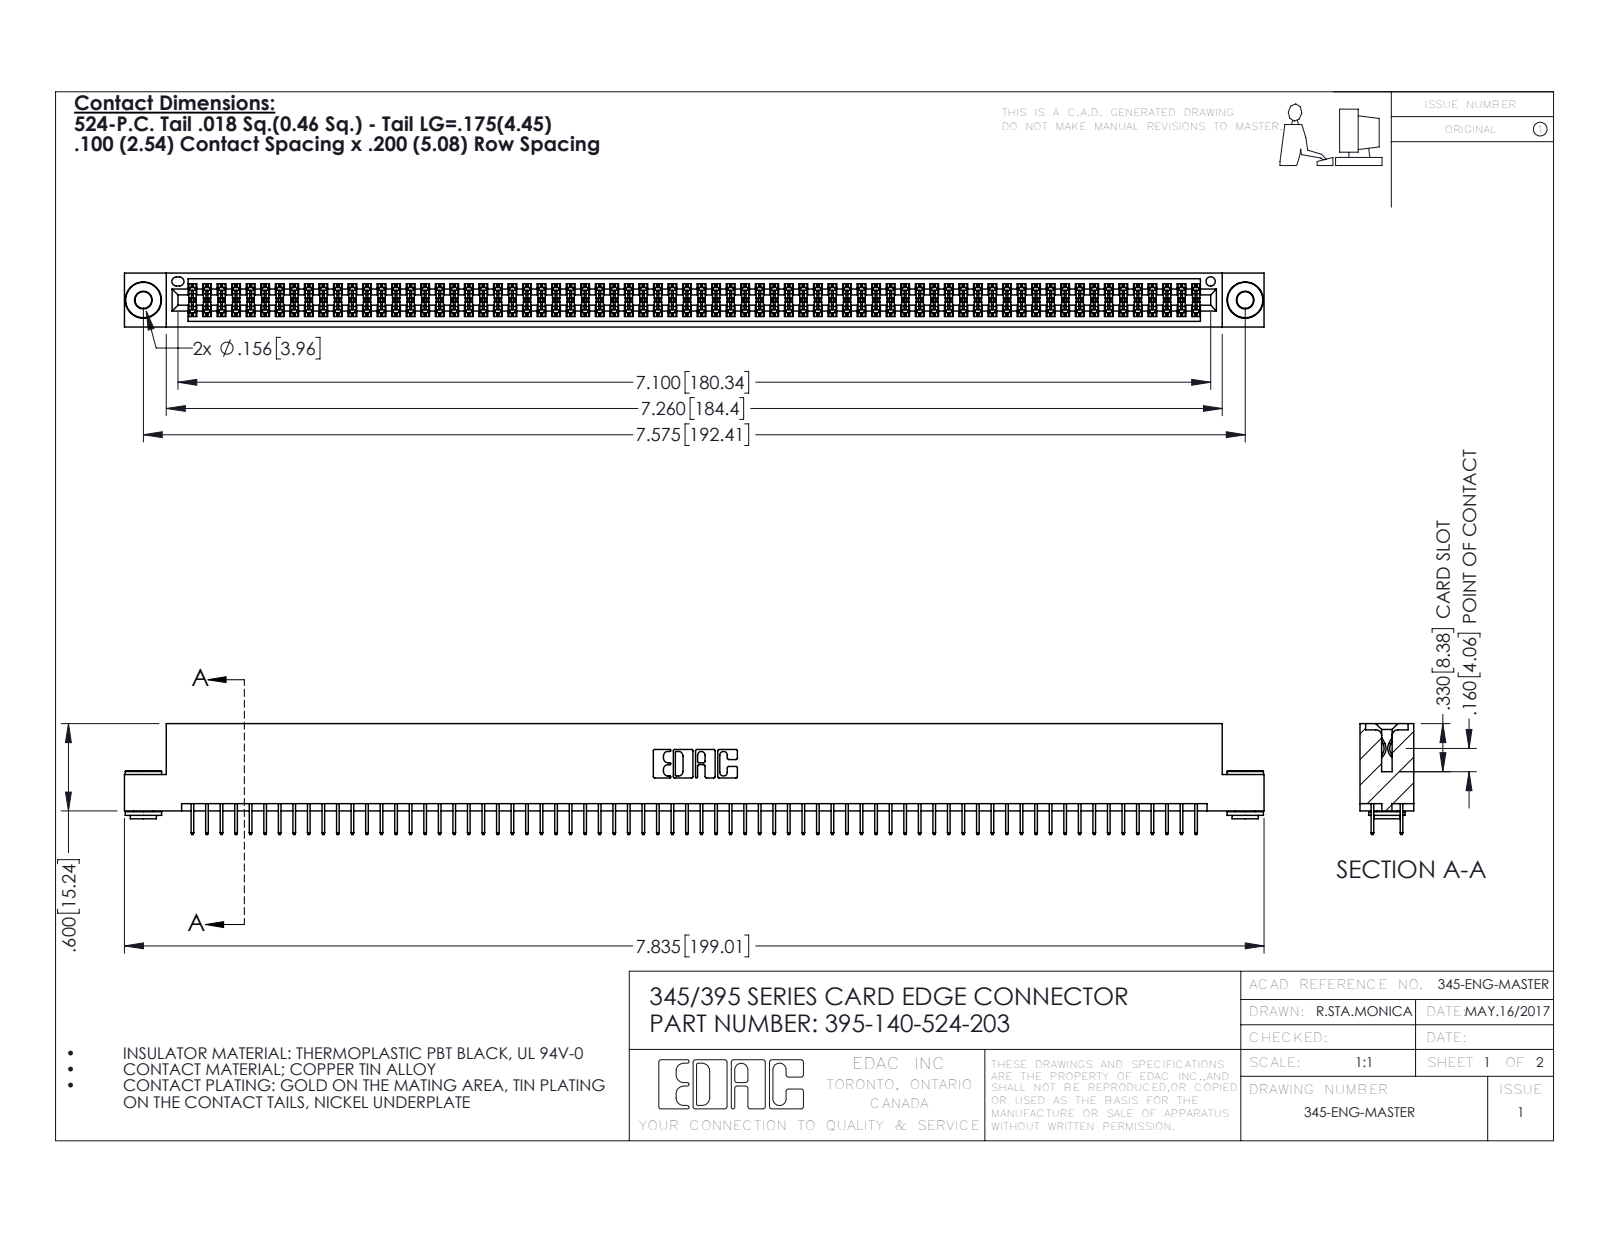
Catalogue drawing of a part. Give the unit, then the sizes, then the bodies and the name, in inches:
Units: inches
Overall size (bounding box): 7.835 × 0.762 × 0.37
Round holes (diameter × count): ⌀0.116 ×2, ⌀0.156 ×2, ⌀0.064 ×1
Round bosses / shafts (diameter × count): ⌀0.25 ×2, ⌀0.18 ×2, ⌀0.136 ×2
Partial cylindrical surfaces — rounded edges, fillets, slot ends (radius × count): R0.006 ×210, R0.01 ×22, R0.007 ×6, R0.031 ×6, R0.026 ×3, R0.014 ×2, R0.019 ×2, R0.022 ×2
Main face-to-face distances: 0.072, 0.298, 0.2, 0.37, 0.025, 0.098, 0.272, 0.225, 0.072, 0.175
Hole centre spacings: 0.27, 7.339, 7.575
Volume: 1.184 in³ · Surface area: 44.74 in²
Bodies: 143 solids, 7724 faces (5550 planar, 2166 cylindrical, 8 other)
Part name (STEP PRODUCT): 395-140-524-203; 345-292-001_345-293-124; 345 Part_Flush Mounting Lugs - 0.156 Dia-TH; 345-250-002_345-250-002-102
STEP written by: SolidWorks 2016 (CONFIG_CONTROL_DESIGN)
